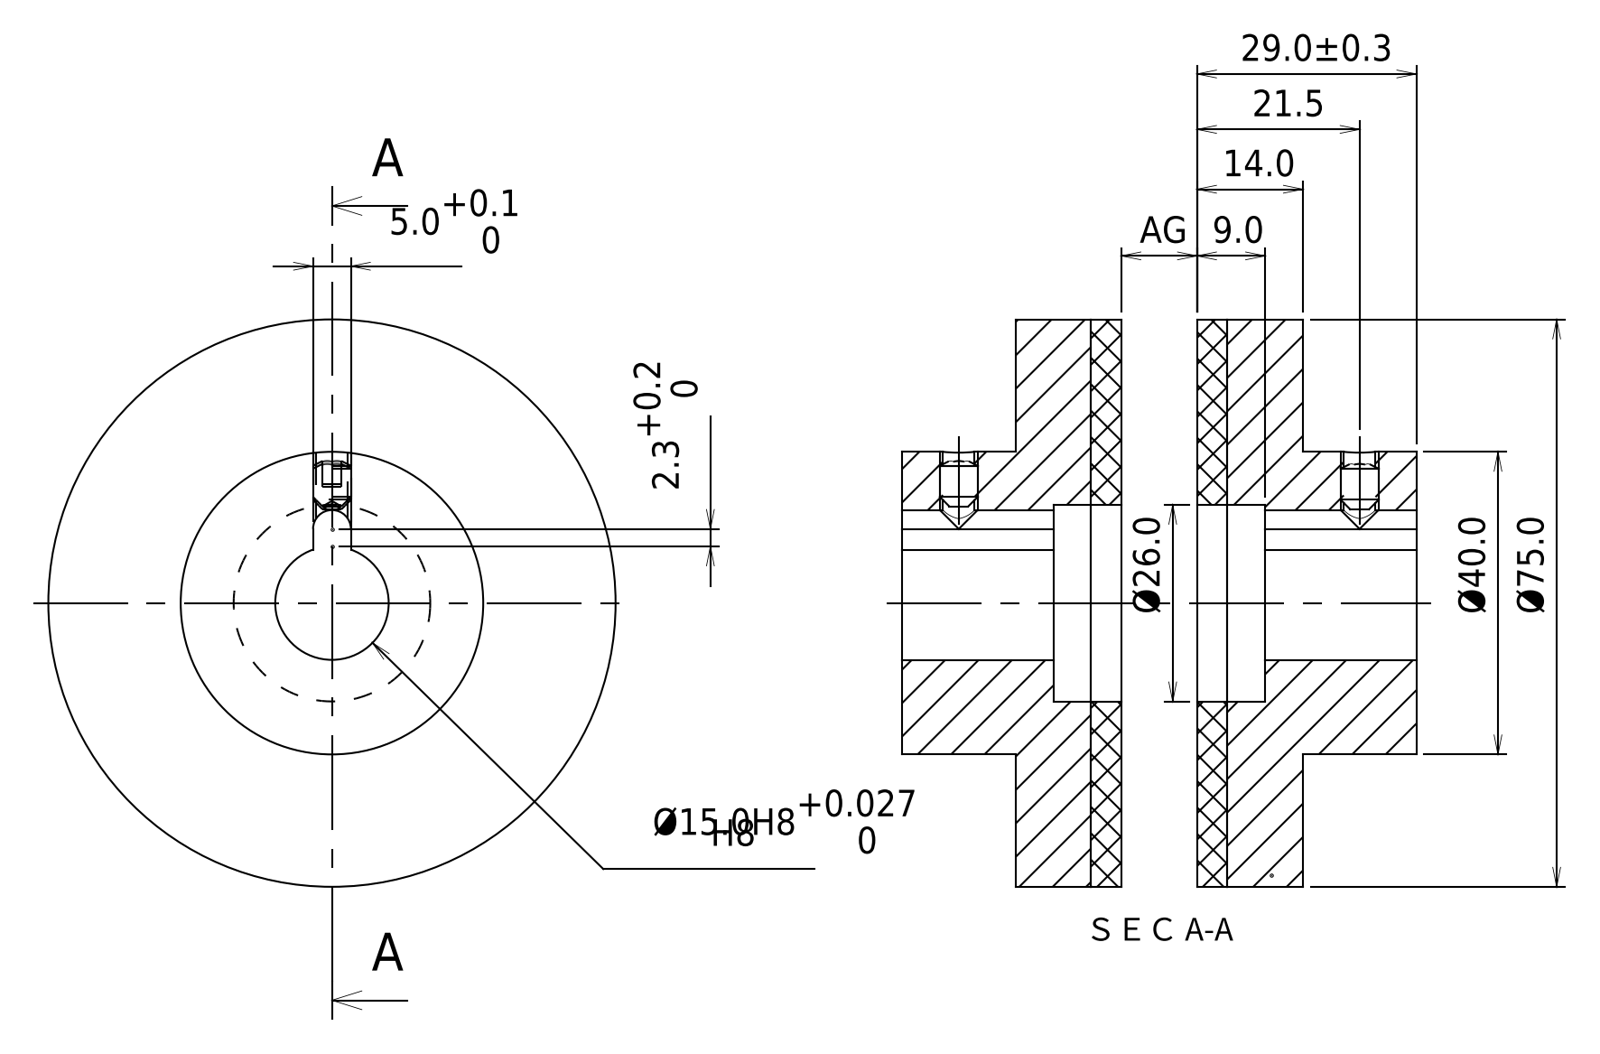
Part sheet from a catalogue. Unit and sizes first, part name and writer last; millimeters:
Units: millimetres
Overall size (bounding box): 75 × 75 × 29
Round holes (diameter × count): ⌀4.2 ×1, ⌀15 ×1, ⌀26 ×1
Round bosses / shafts (diameter × count): ⌀75 ×1, ⌀40 ×1, ⌀5 ×1
Partial cylindrical surfaces — rounded edges, fillets, slot ends (radius × count): R2.5 ×1
Main face-to-face distances: 4, 14, 10, 29, 25, 15, 5, 9, 20, 2.5
Volume: 72 007 mm³ · Surface area: 23 593 mm²
Bodies: 4 solids, 38 faces (22 planar, 10 cylindrical, 6 other)
STEP written by: PSStep 10.0 (CONFIG_CONTROL_DESIGN)
